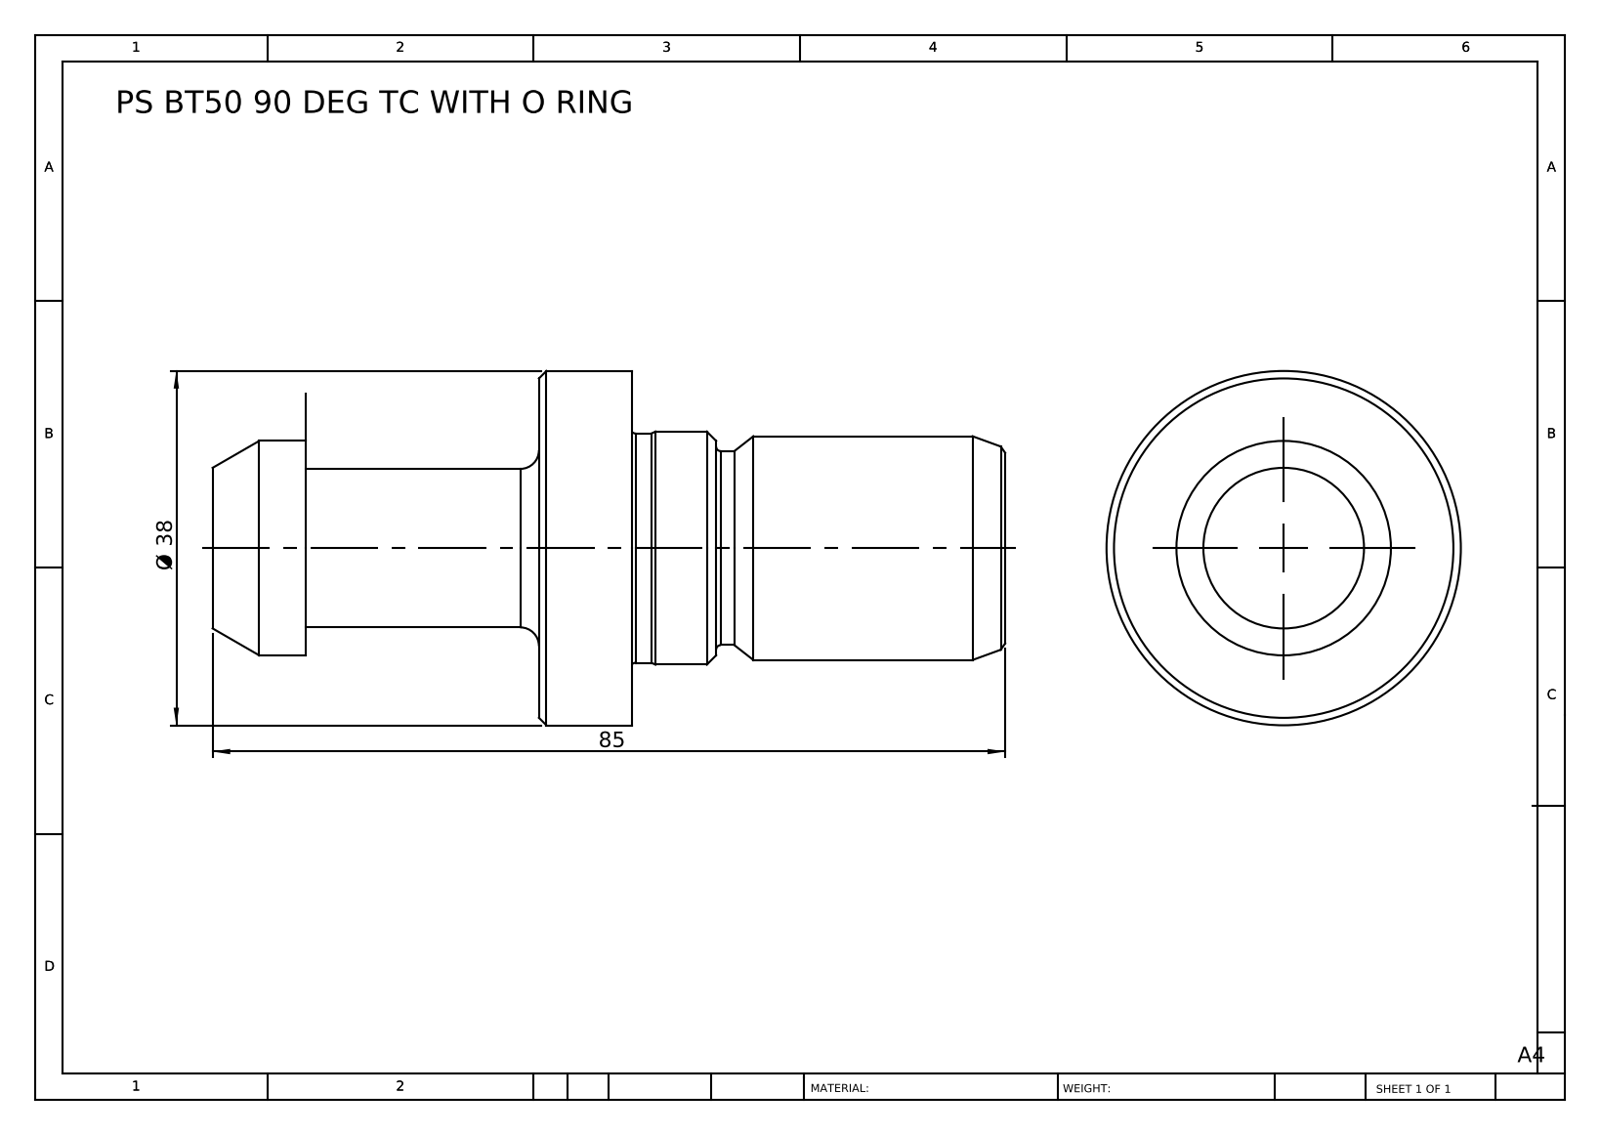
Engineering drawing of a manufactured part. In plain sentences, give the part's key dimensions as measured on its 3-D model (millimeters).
The part is named "PS BT50 90 DEG TC WITH O RING". Its 3-D file was written by "SolidWorks 2014 (CONFIG_CONTROL_DESIGN)". It is 1 solid with 42 faces: 6 planar, 14 cylindrical and 22 other. Overall it measures 85 by 38 by 38 millimeters. Its volume is 38 561 cubic millimeters and its surface area 8 633 square millimeters. Round bosses or shafts: 1 of diameter 38, 1 of diameter 25, 1 of diameter 24.6, 1 of diameter 24, 1 of diameter 23, 1 of diameter 20.8, 1 of diameter 17. The main face-to-face distances are 10, 35, 40, 50, 85, 45, 75, 25, 31, 9.
